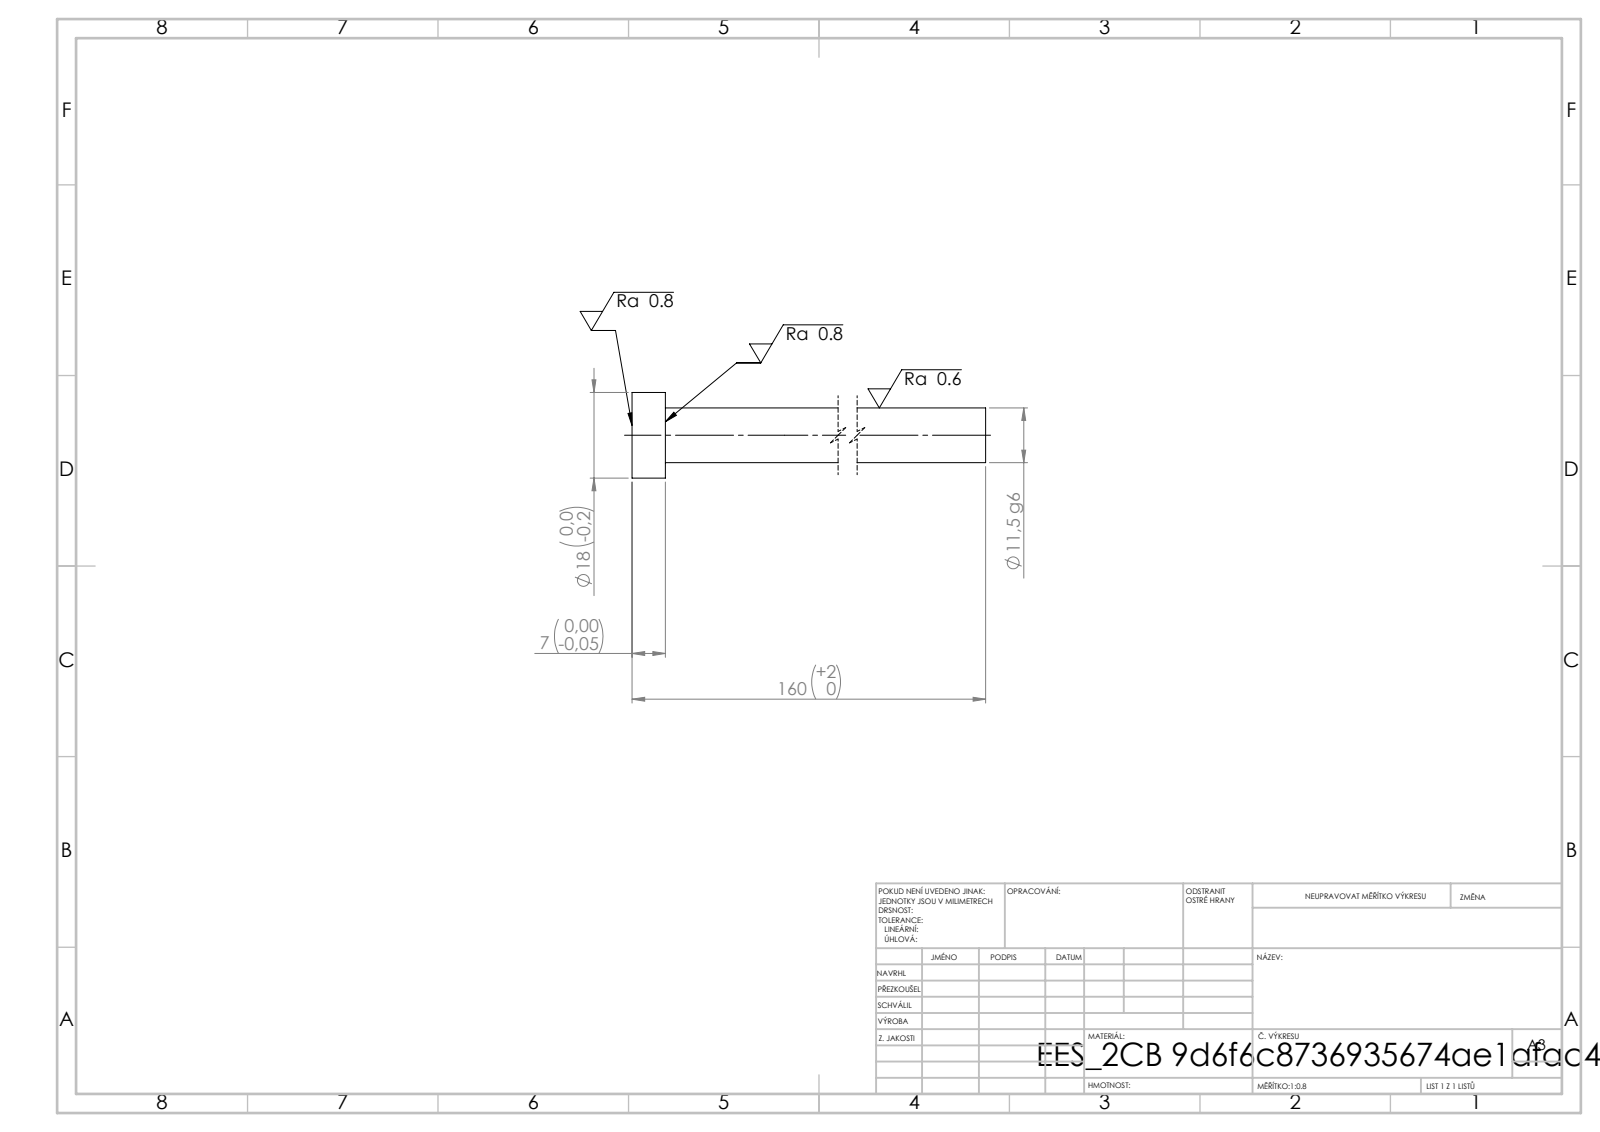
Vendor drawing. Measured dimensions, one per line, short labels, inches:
written by: SolidWorks 2019 (CONFIG_CONTROL_DESIGN)
unit: in
bodies: 1 solid, 7 faces (3 planar, 4 cylindrical, 0 other)
size: 6.299 × 0.709 × 0.709
volume: 1.078 in³; area: 9.97 in²
bosses: 1× ⌀0.709, 1× ⌀0.453
face distances: 0.276, 6.299, 6.024
